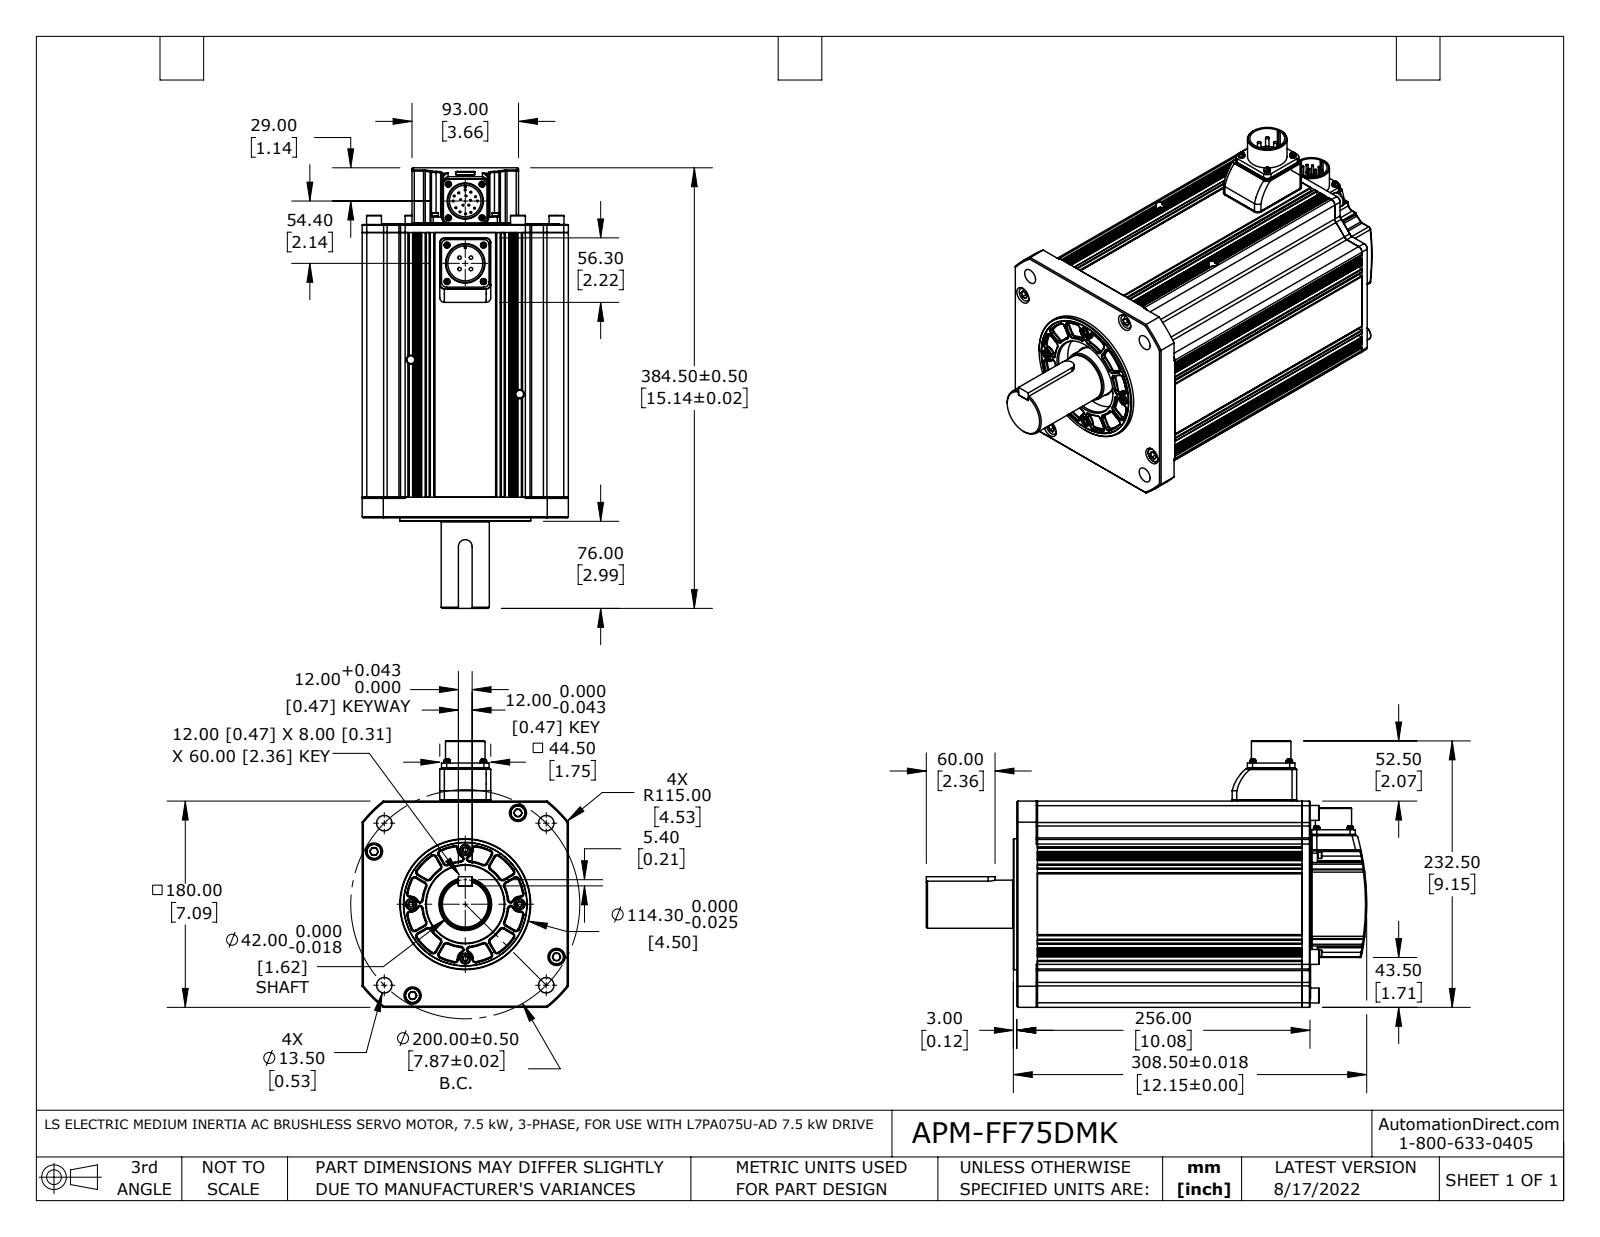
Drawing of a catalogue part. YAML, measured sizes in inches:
part_name: "FM18GA001G04_Out Line(APM-FF75D_K) r1 nc fxt"
step_written_by: "SolidWorks 2017 (AUTOMOTIVE_DESIGN)"
units: inches
bodies: {solids: 57, faces: 2355, planar: 795, cylindrical: 874, other: 686}
overall_size: [15.138, 9.154, 7.087]
volume: 472.3
surface_area: 873.9
round_holes:
  - {diameter: 0.118, count: 12}
  - {diameter: 0.098, count: 8}
  - {diameter: 0.12, count: 8}
  - {diameter: 0.236, count: 8}
  - {diameter: 0.374, count: 8}
  - {diameter: 0.268, count: 6}
  - {diameter: 0.138, count: 4}
  - {diameter: 0.142, count: 4}
  - {diameter: 0.146, count: 4}
  - {diameter: 0.197, count: 4}
  - {diameter: 0.354, count: 4}
  - {diameter: 0.362, count: 4}
round_bosses_or_shafts:
  - {diameter: 0.063, count: 17}
  - {diameter: 0.213, count: 8}
  - {diameter: 0.52, count: 4}
  - {diameter: 0.512, count: 4}
  - {diameter: 0.335, count: 4}
  - {diameter: 0.315, count: 4}
  - {diameter: 0.217, count: 4}
  - {diameter: 0.118, count: 4}
partial_cylinders:
  - {radius: 0.02, count: 124}
  - {radius: 0.098, count: 56}
  - {radius: 0.157, count: 24}
  - {radius: 0.079, count: 17}
  - {radius: 0.039, count: 14}
  - {radius: 0.177, count: 12}
  - {radius: 0.256, count: 4}
  - {radius: 0.012, count: 2}
face_to_face_distances: [9.094, 7.087, 0.039, 0.295, 0.709, 1.319, 5.768, 0.315, 0.394, 0.276]
hole_center_spacings: [1.282, 2.93, 5.423, 0.042, 0.819, 0.885, 0.927, 1.035]
